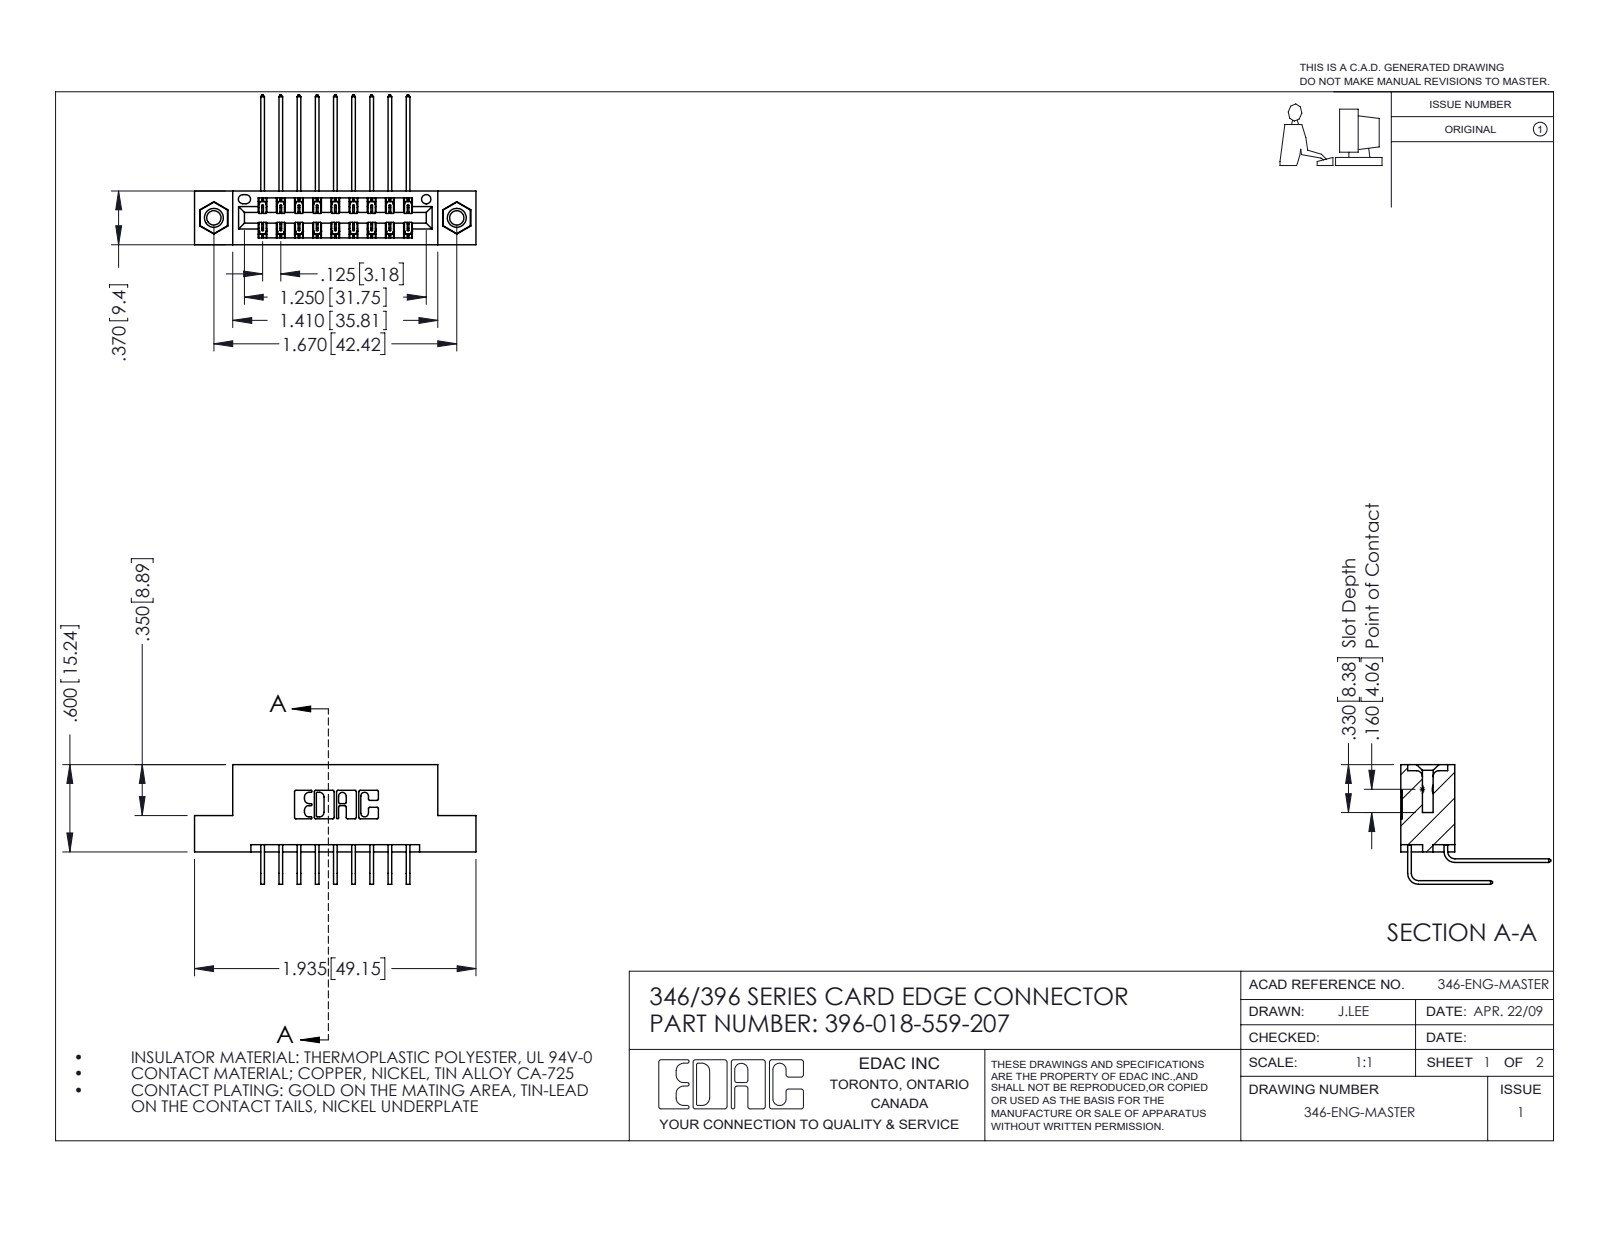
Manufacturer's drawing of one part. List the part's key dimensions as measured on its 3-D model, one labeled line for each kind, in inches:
Part name (STEP PRODUCT): 396-018-559-207; 345-250-001_345-250-005-103; 345-292-001_558 559 Tail - 1; 346 Part_Flush Mounting Lugs - 0.156 Dia-TI (+1 more)
STEP written by: SolidWorks 2016 (CONFIG_CONTROL_DESIGN)
Units: inches
Bodies: 21 solids, 1154 faces (774 planar, 364 cylindrical, 16 other)
Overall size (bounding box): 1.935 × 1.03 × 0.823
Volume: 0.282 in³ · Surface area: 9.878 in²
Round holes (diameter × count): ⌀0.098 ×2, ⌀0.125 ×2, ⌀0.156 ×2, ⌀0.064 ×1
Round bosses / shafts (diameter × count): ⌀0.155 ×2
Partial cylindrical surfaces — rounded edges, fillets, slot ends (radius × count): R0.006 ×27, R0.01 ×22, R0.007 ×6, R0.031 ×6, R0.026 ×3, R0.014 ×2, R0.022 ×2, R0.024 ×2
Main face-to-face distances: 0.25, 0.048, 0.322, 0.37, 0.025, 0.072, 0.298, 0.125, 0.275, 0.148
Hole centre spacings: 0.246, 1.465, 1.67
